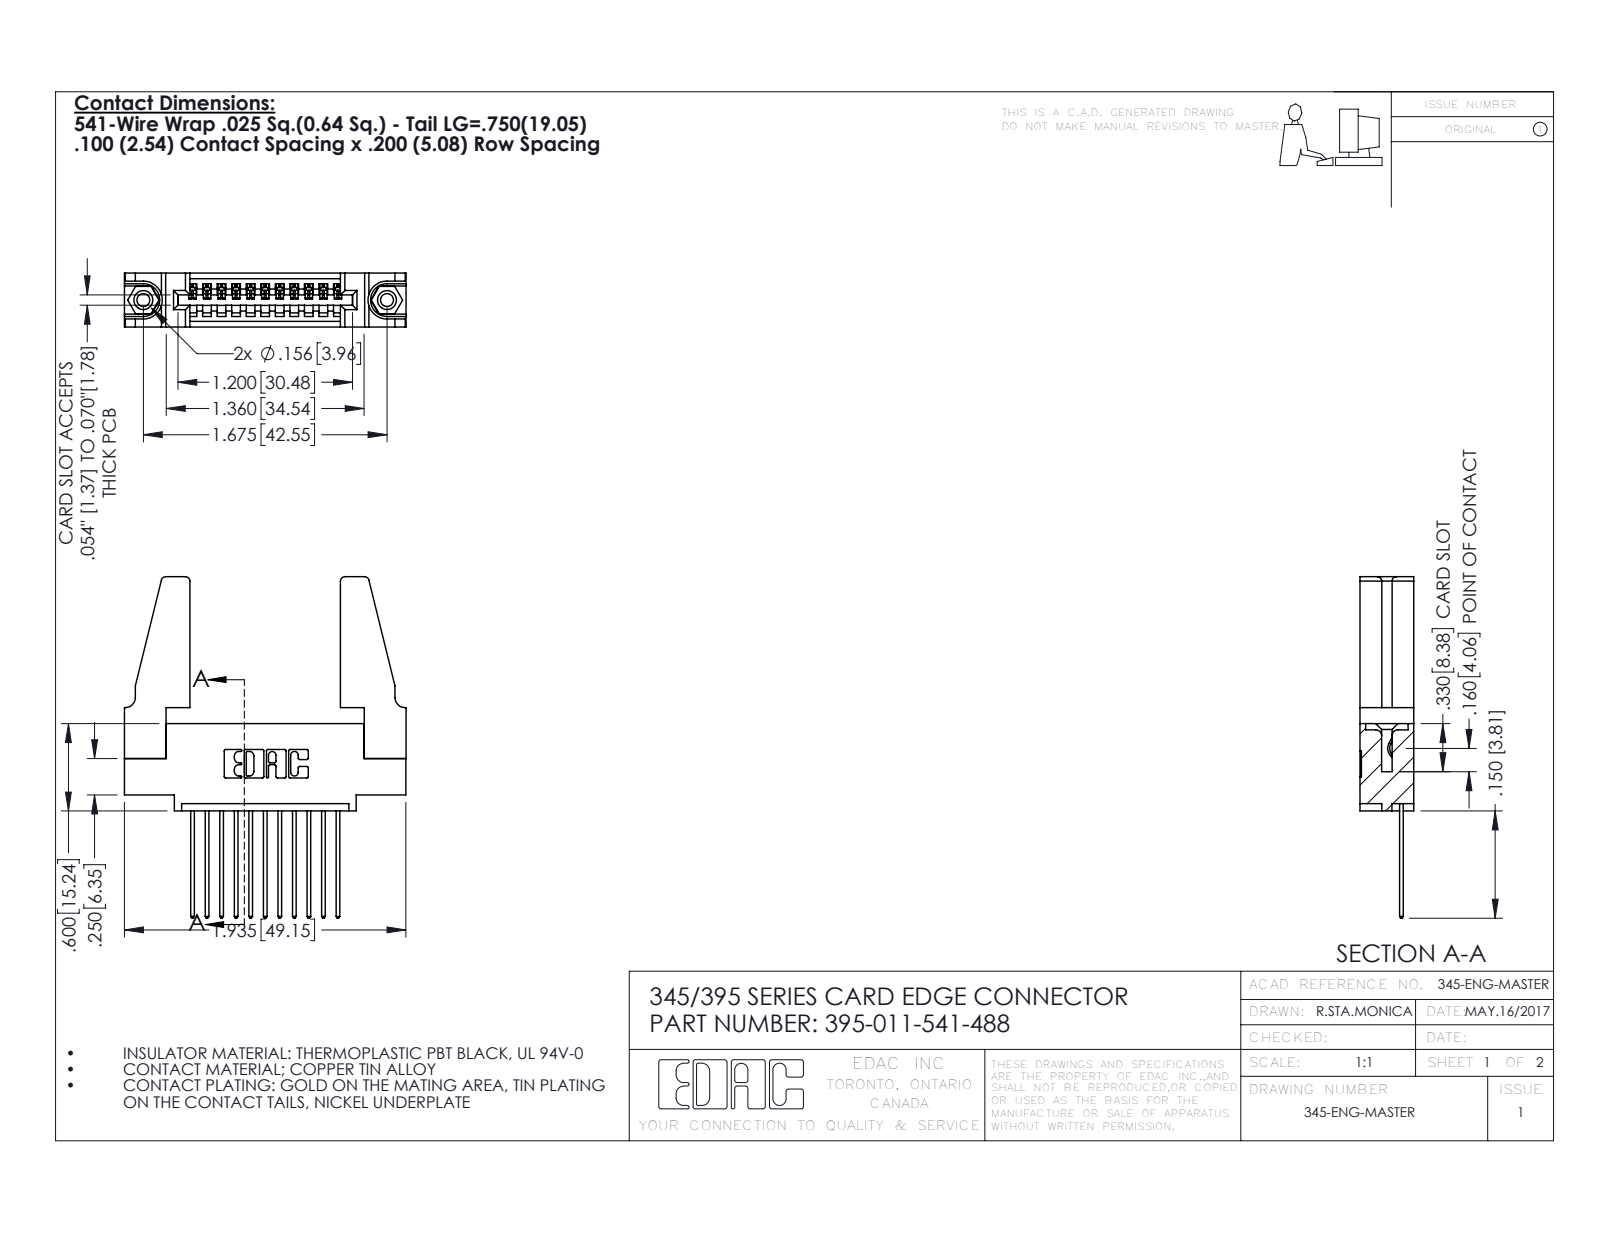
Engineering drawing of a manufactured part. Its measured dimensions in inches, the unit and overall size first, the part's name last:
Units: inches
Overall size (bounding box): 2.347 × 1.936 × 0.37
Round holes (diameter × count): ⌀0.089 ×2, ⌀0.125 ×2, ⌀0.156 ×2, ⌀0.064 ×1
Round bosses / shafts (diameter × count): ⌀0.155 ×2
Partial cylindrical surfaces — rounded edges, fillets, slot ends (radius × count): R0.006 ×22, R0.01 ×22, R0.01 ×22, R0.03 ×8, R0.007 ×6, R0.031 ×6, R0.026 ×3, R0.031 ×2
Main face-to-face distances: 0.37, 0.072, 0.298, 0.098, 0.272, 0.025, 0.2, 0.225, 0.148, 0.15
Hole centre spacings: 0.27, 1.443, 1.675
Volume: 0.466 in³ · Surface area: 13.68 in²
Bodies: 16 solids, 892 faces (596 planar, 280 cylindrical, 16 other)
Part name (STEP PRODUCT): 395-011-541-488; 345-250-001_345-250-001-102; 345 Part_0.110 Offset - 0.156 Dia-TH; 345-220-078_345-220-088 (+1 more)
STEP written by: SolidWorks 2016 (CONFIG_CONTROL_DESIGN)
